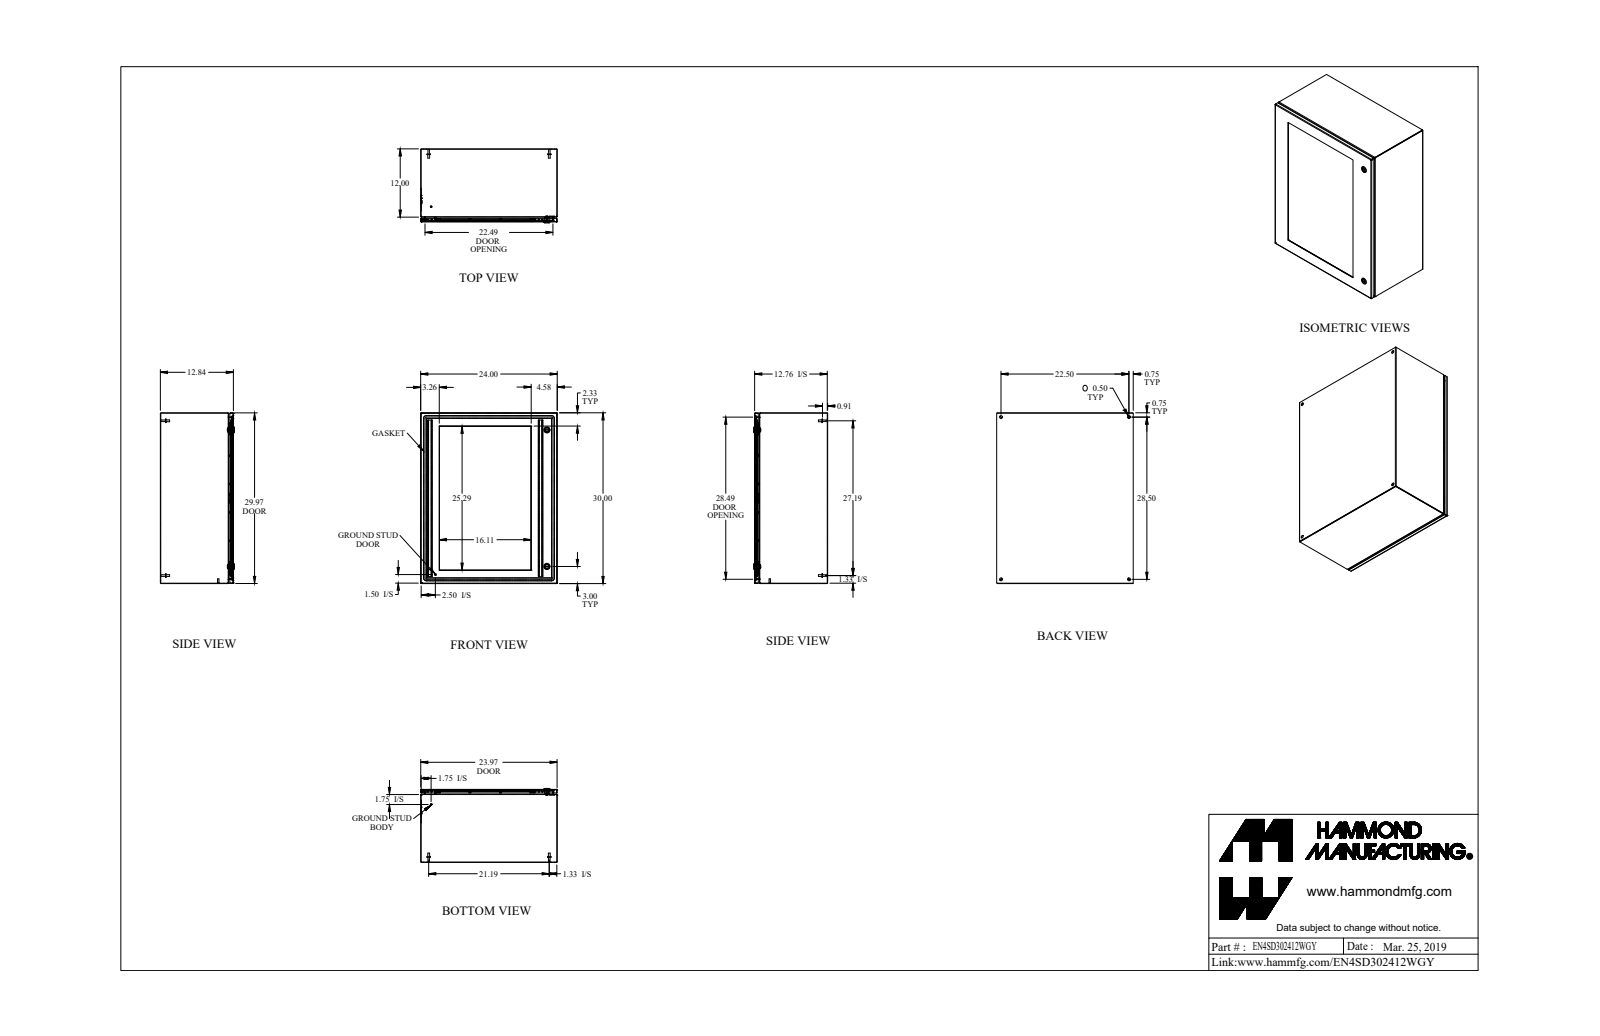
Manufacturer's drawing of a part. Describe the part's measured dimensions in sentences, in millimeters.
The part is named "EN4SD302412WGY". Its 3-D file was written by "SolidWorks 2019 (AUTOMOTIVE_DESIGN)". It is 82 solids with 1603 faces: 810 planar, 499 cylindrical and 294 other. Overall it measures 762 by 609.6 by 330.1 millimeters. Its volume is 5 118 000 cubic millimeters and its surface area 4 318 000 square millimeters. Round holes: 20 of diameter 3.3, 20 of diameter 6.4, 4 of diameter 12.7, 2 of diameter 5.9, 2 of diameter 15.9, 2 of diameter 19.9, 1 of diameter 4.4, 1 of diameter 6.1, 1 of diameter 6.1. Round bosses or shafts: 21 of diameter 5.7, 20 of diameter 9.3, 20 of diameter 4.2, 4 of diameter 15.9, 4 of diameter 8, 4 of diameter 6.9, 2 of diameter 27.9, 2 of diameter 13.3. Partial cylindrical surfaces (rounded edges, fillets, slot ends): 14 of radius 0.9, 14 of radius 2.7, 12 of radius 1.1, 12 of radius 2.1, 12 of radius 3.2, 12 of radius 7.9, 8 of radius 2.5, 6 of radius 0.2. The main face-to-face distances are 1.8, 324.2, 322.4, 607.8, 760.2, 316.1, 6.4, 317.9, 605.9, 609.6. The hole center spacings are 252.7, 503.5, 126.4, 136.4, 422.8, 435.5, 453.4, 682.6.
